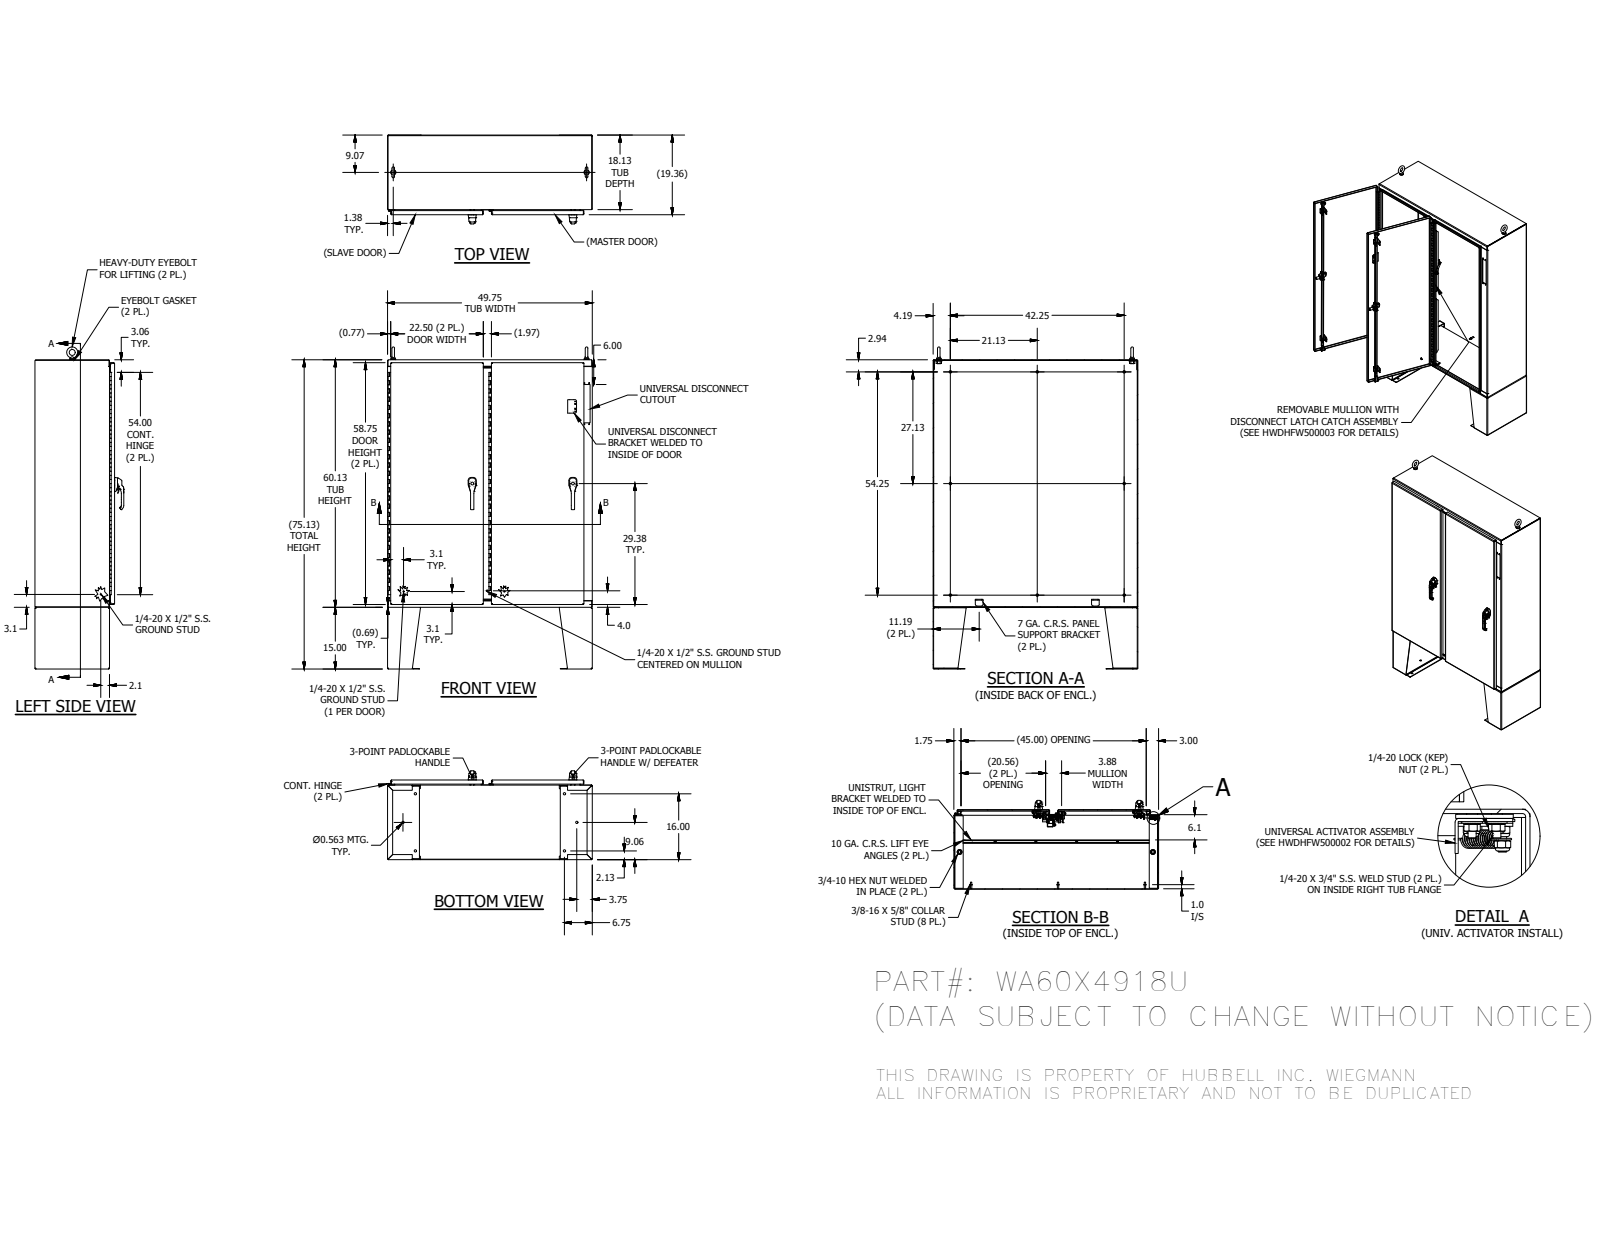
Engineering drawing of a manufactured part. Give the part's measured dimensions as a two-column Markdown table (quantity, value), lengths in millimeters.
| quantity | value |
| --- | --- |
| part name | WA60X4918UBLR; WAX4918UTOP; WAX4918UBTM; HFW332010S (+8 more) |
| STEP written by | Autodesk Inventor 2016 (AUTOMOTIVE_DESIGN) |
| units | millimeters |
| bodies | 212 solids, 8687 faces (3990 planar, 2936 cylindrical, 1761 other) |
| overall size | 1987.49 × 1263.65 × 548.85 |
| volume | 28 680 000 mm³ |
| surface area | 17 590 000 mm² |
| round holes (diameter × count) | 6.35 × 18, 9.52 × 18, 14.29 × 18, 4.83 × 8, 5.08 × 8, 5.16 × 8, 7.02 × 8, 7.33 × 8, 7.94 × 8, 8.51 × 8, 9.65 × 8, 5.11 × 7 |
| round bosses / shafts (diameter × count) | 6.35 × 24, 8.38 × 18, 15.88 × 13, 8.56 × 12, 9.52 × 11, 14.29 × 9, 25.4 × 8, 11.13 × 8 |
| partial cylindrical surfaces (radius × count) | 0.5 × 333, 0.3 × 203, 0.51 × 192, 0.47 × 42, 1.27 × 40, 3.17 × 37, 2.38 × 35, 1.59 × 27 |
| main face-to-face distances | 3.4, 488.1, 3.41, 484.7, 491.5, 1260.24, 1523.77, 1256.84, 1263.64, 3.17 |
| hole center spacings | 0.62, 50.8, 621.5, 0.63, 621.91, 27.99, 28, 40.66 |
